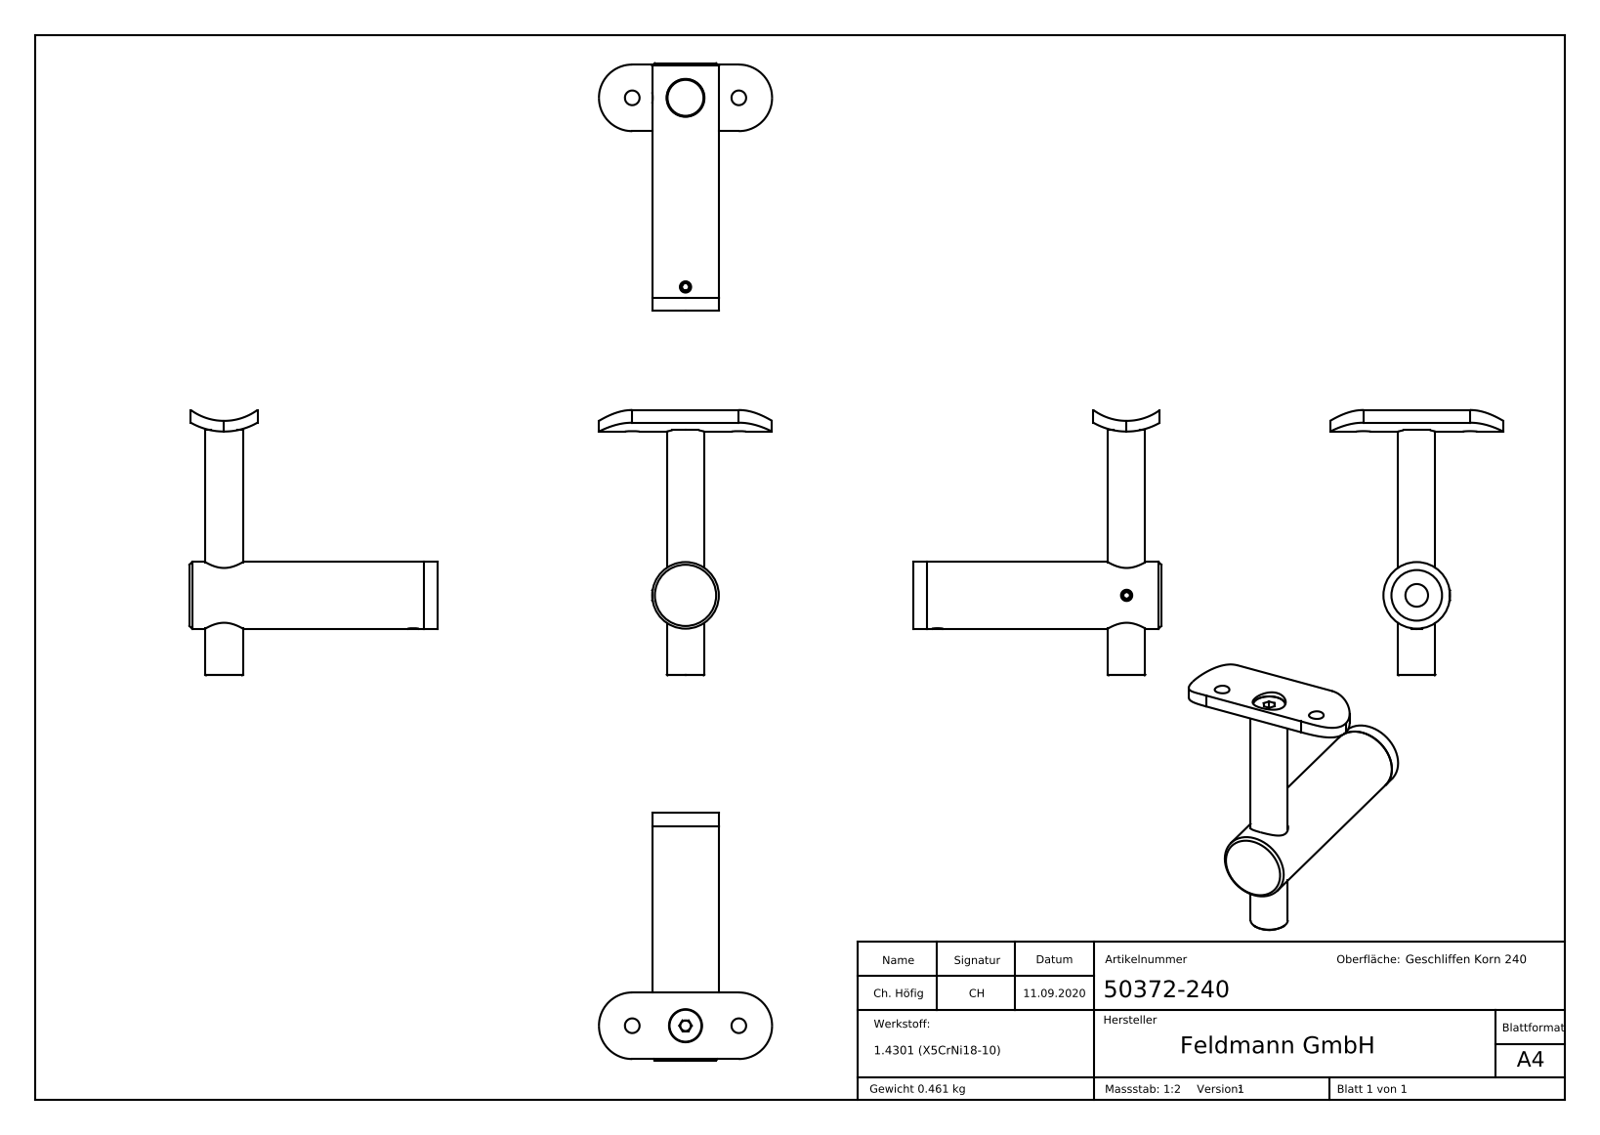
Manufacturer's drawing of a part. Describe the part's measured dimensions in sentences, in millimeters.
The part is named "DIN913; 5037X-240 Teil2_50372-240 Teil2; 50372-240; 5037X-240 Teil4 (+8 more)". Its 3-D file was written by "SolidWorks 2018 (CONFIG_CONTROL_DESIGN)". It is 7 solids with 348 faces: 146 planar, 72 cylindrical and 130 other. Overall it measures 99.58 by 93 by 88 millimeters. Its volume is 58 348 cubic millimeters and its surface area 21 553 square millimeters. Round holes: 2 of diameter 4.2, 2 of diameter 5.5, 1 of diameter 5, 1 of diameter 8, 1 of diameter 8.5, 1 of diameter 12.4, 1 of diameter 14, 1 of diameter 14.2, 1 of diameter 16, 1 of diameter 19. Round bosses or shafts: 2 of diameter 5, 1 of diameter 25, 1 of diameter 12, 1 of diameter 6. Partial cylindrical surfaces (rounded edges, fillets, slot ends): 2 of radius 12.5, 1 of radius 8.1, 1 of radius 21.2, 1 of radius 25.2. The main face-to-face distances are 88, 3, 91, 5, 2, 93, 67.5, 92.5, 65.5, 90.5. The hole center spacings are 20, 73.76, 40, 71.
